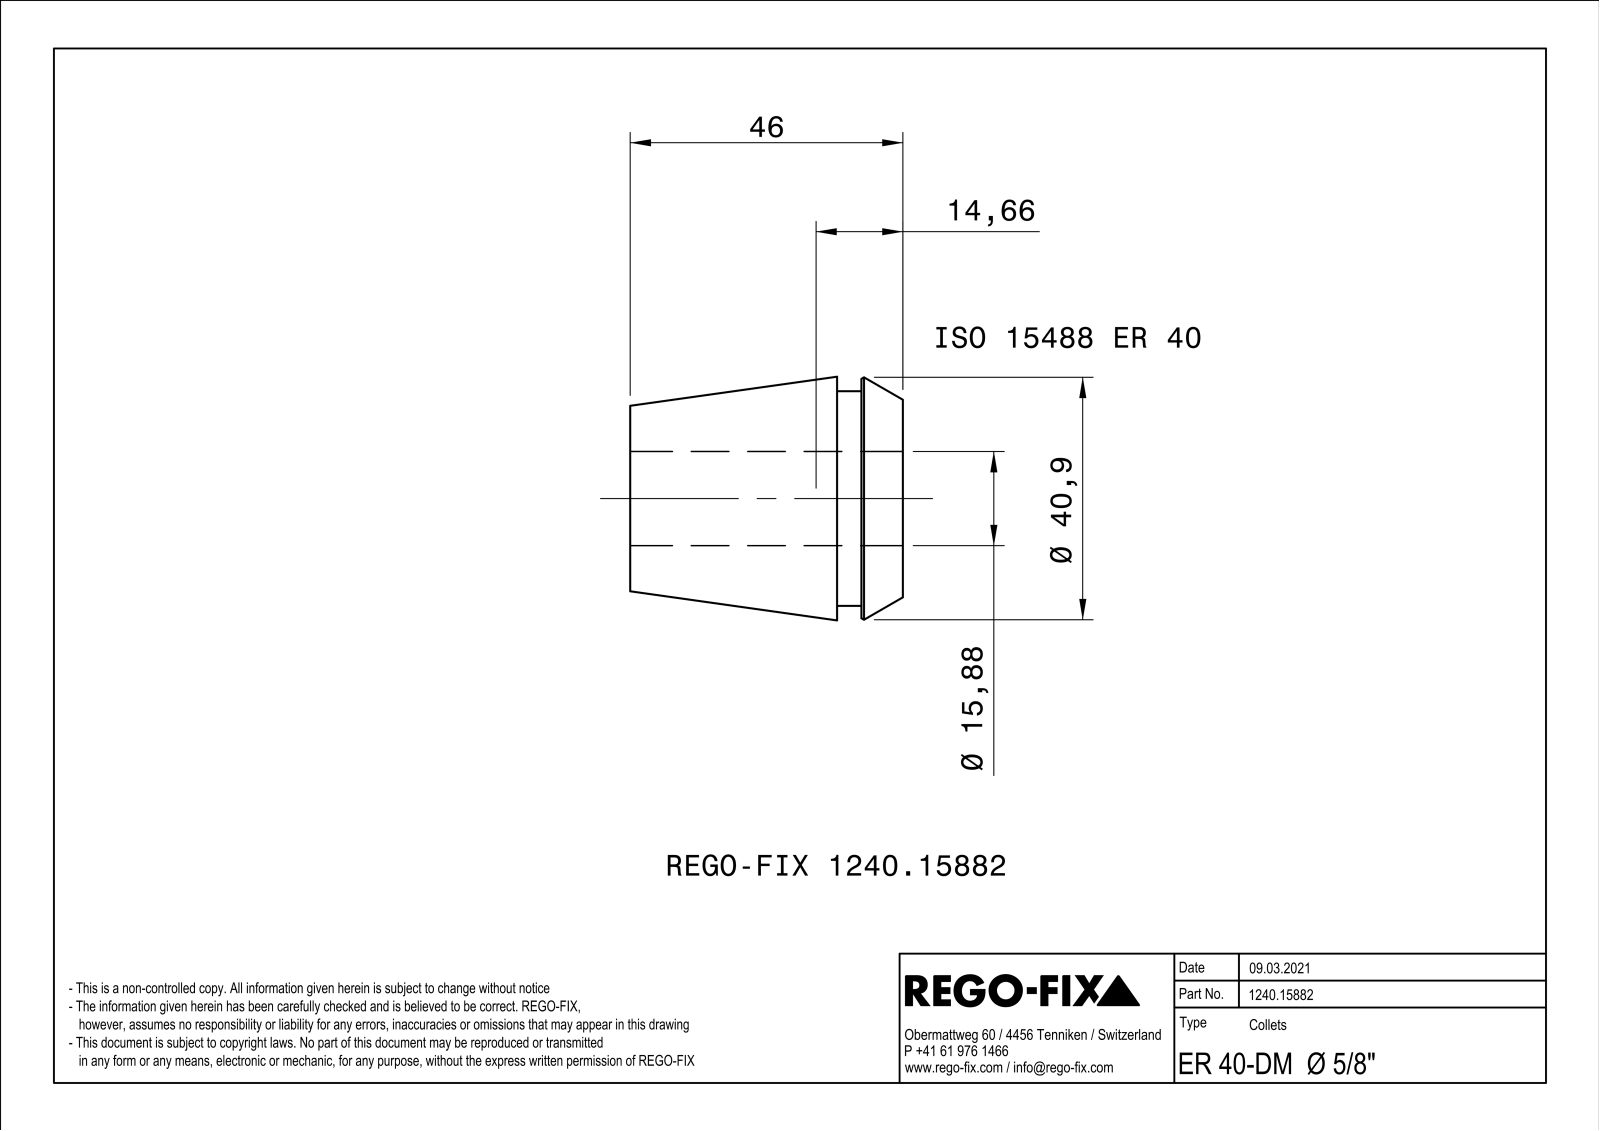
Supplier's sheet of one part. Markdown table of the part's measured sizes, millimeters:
| quantity | value |
| --- | --- |
| part name | NOCUT |
| STEP written by | SIEMENS PLM Software Solid Edge ST10 (AUTOMOTIVE_DESIGN) |
| units | millimeters |
| bodies | 1 solid, 154 faces (80 planar, 9 cylindrical, 65 other) |
| overall size | 46 × 40.99 × 40.99 |
| volume | 33 045 mm³ |
| surface area | 19 686 mm² |
| round holes (diameter × count) | 15.88 × 1 |
| round bosses / shafts (diameter × count) | 36.2 × 1 |
| main face-to-face distances | 1, 46, 11.1, 34.9, 7, 4.1, 39, 17, 10, 5.9 |
